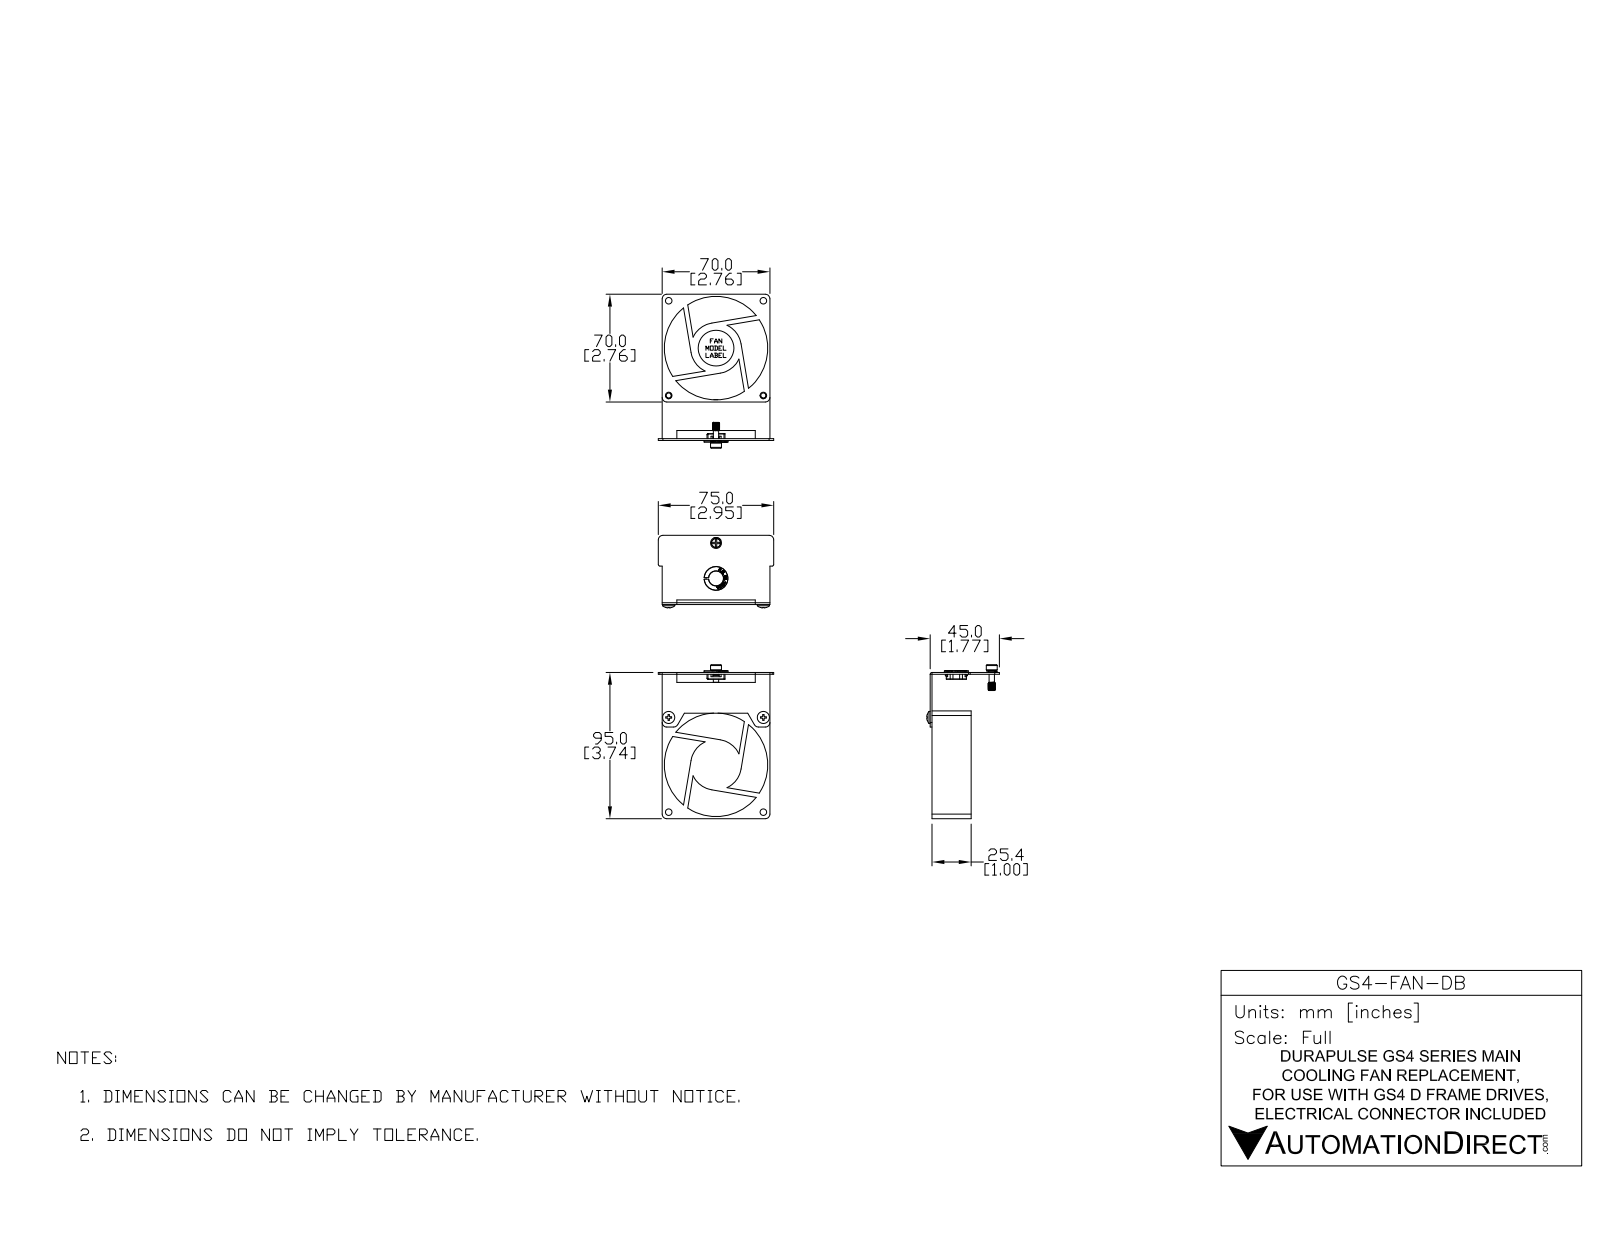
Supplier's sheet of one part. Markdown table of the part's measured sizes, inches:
| quantity | value |
| --- | --- |
| part name | GS4-FAN-DB1 Screw Only A; GS4-FAN-DB1 Grommet A; GS4-FAN-DB A; GS4-FAN-DB1 |
| STEP written by | SolidWorks 2016 (AUTOMOTIVE_DESIGN) |
| units | inches |
| bodies | 4 solids, 462 faces (197 planar, 103 cylindrical, 162 other) |
| overall size | 3.943 × 2.953 × 1.89 |
| volume | 2.701 in³ |
| surface area | 56.6 in² |
| round holes (diameter × count) | 0.169 × 4, 0.157 × 1, 0.378 × 1, 0.406 × 1, 0.512 × 1, 2.646 × 1 |
| round bosses / shafts (diameter × count) | 0.276 × 2, 0.169 × 2, 2.724 × 1, 1.299 × 1, 0.61 × 1, 0.28 × 1, 0.177 × 1, 0.136 × 1 |
| partial cylindrical surfaces (radius × count) | 0.118 × 8, 0.004 × 5, 0.047 × 5, 0.098 × 4, 0.138 × 2, 0.029 × 1, 0.242 × 1, 0.258 × 1 |
| main face-to-face distances | 0.047, 1, 1, 1.048, 0.048, 0.2, 0.843, 0.157, 0.843, 0.89 |
| hole center spacings | 2.421, 1.712, 1.712, 3.424, 0.906 |
